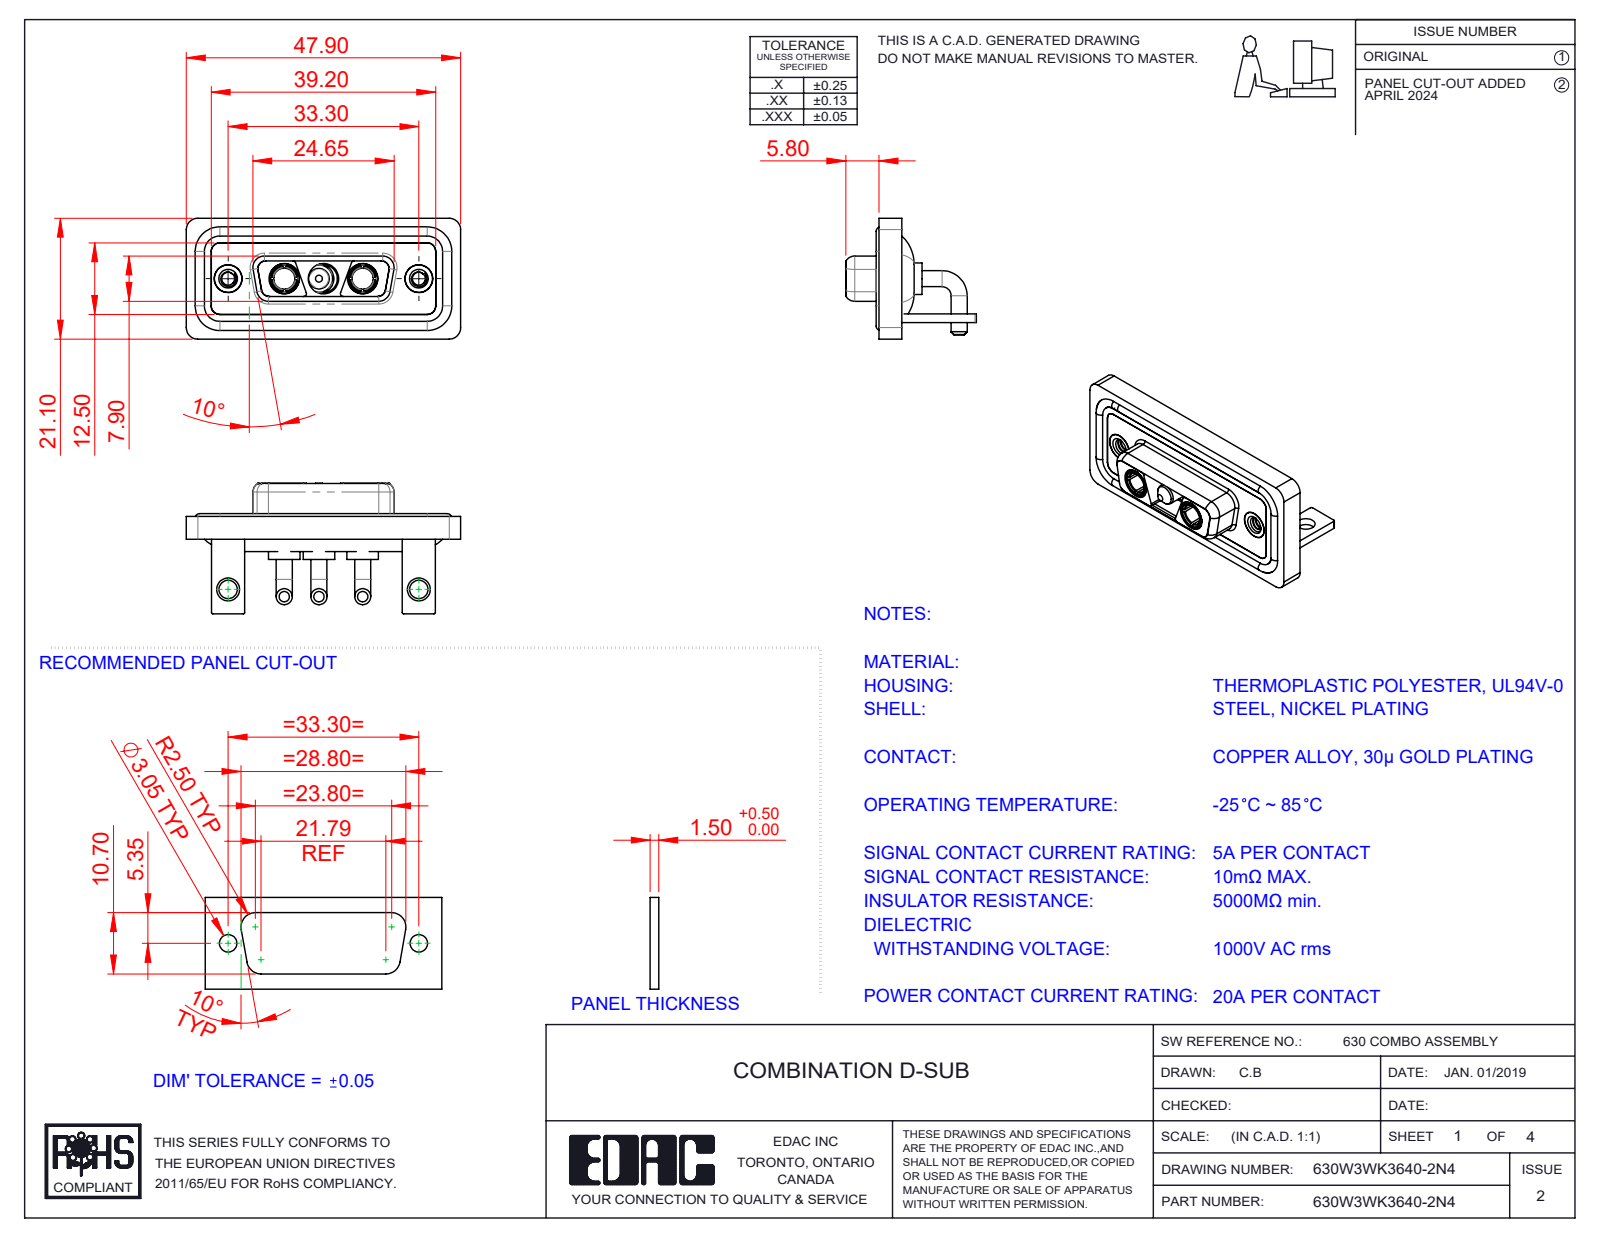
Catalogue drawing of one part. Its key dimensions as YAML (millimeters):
part_name: "630Combo Stabilizer Bracket_50 Contacts; 630Combo Shell Front_15 Contacts; Power Pin_20A RA; 630Combo Waterproof Housing_15 Contacts (+5 more)"
step_written_by: "SolidWorks 2023 (CONFIG_CONTROL_DESIGN)"
units: millimeters
bodies: {solids: 15, faces: 643, planar: 198, cylindrical: 288, other: 157}
overall_size: [47.9, 22.8, 21.1]
volume: 6398
surface_area: 10474
round_holes:
  - {diameter: 4.85, count: 5}
  - {diameter: 5.3, count: 3}
  - {diameter: 2.26, count: 2}
  - {diameter: 3.2, count: 2}
  - {diameter: 3.7, count: 2}
  - {diameter: 4, count: 2}
  - {diameter: 4.05, count: 2}
  - {diameter: 5, count: 2}
round_bosses_or_shafts:
  - {diameter: 2.8, count: 6}
  - {diameter: 1.6, count: 4}
  - {diameter: 5.5, count: 3}
  - {diameter: 5.2, count: 3}
  - {diameter: 4.75, count: 3}
  - {diameter: 3.75, count: 3}
  - {diameter: 4.96, count: 2}
  - {diameter: 4.95, count: 2}
partial_cylinders:
  - {radius: 2, count: 21}
  - {radius: 1.5, count: 18}
  - {radius: 0.25, count: 16}
  - {radius: 1.35, count: 12}
  - {radius: 0.5, count: 9}
  - {radius: 1.6, count: 8}
  - {radius: 0.6, count: 4}
  - {radius: 0.65, count: 4}
face_to_face_distances: [0.4, 2.9, 1.5, 3.7, 1.8, 1.1, 4.1, 1.6, 2.5, 1.4]
hole_center_spacings: [6.85, 9.8, 16.65, 23.5, 33.3, 13.7]
